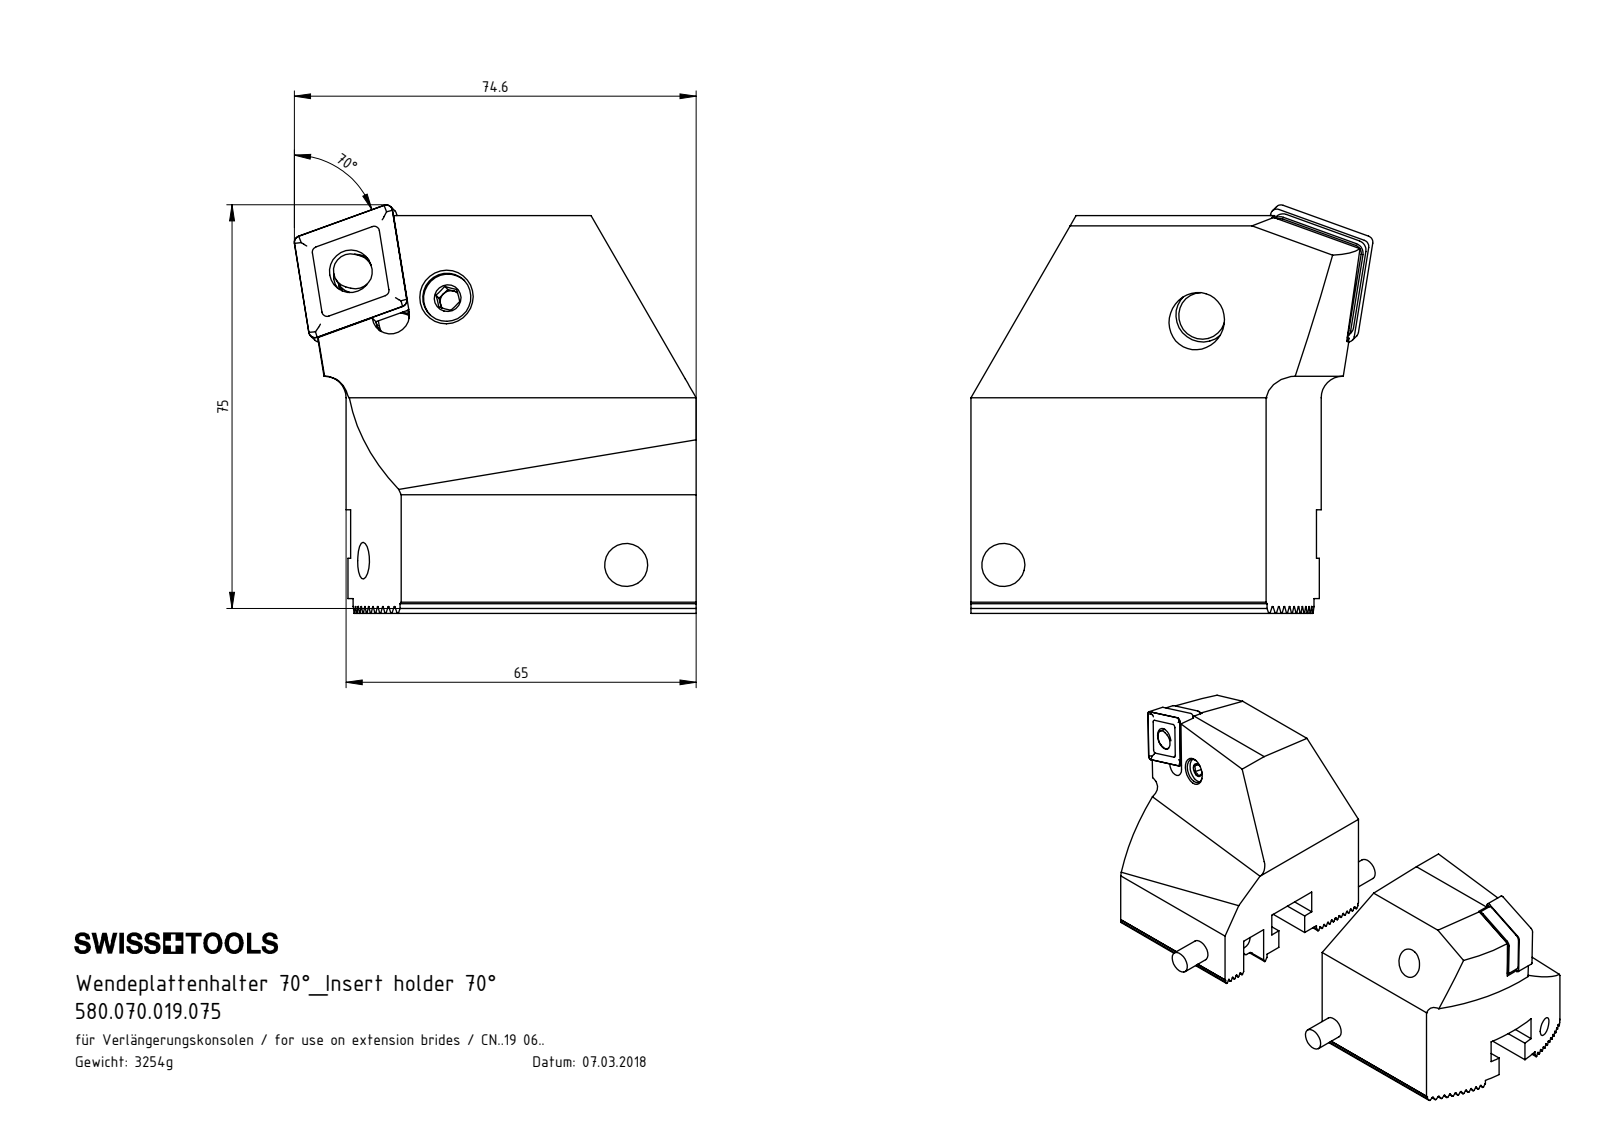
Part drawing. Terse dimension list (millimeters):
name: WCF-ER1.101.000; WCF; WCF-ER3.101.000_A; CNMG190612 (+6 more)
written by: SolidWorks 2017 (CONFIG_CONTROL_DESIGN)
unit: mm
bodies: 18 solids, 1312 faces (784 planar, 172 cylindrical, 356 other)
size: 200.21 × 94 × 75.79
volume: 411 183 mm³; area: 74 323 mm²
holes: 4× ⌀8, 2× ⌀6.8, 2× ⌀7.94, 2× ⌀9, 2× ⌀9.6, 2× ⌀10.2
bosses: 2× ⌀10, 2× ⌀9.9, 2× ⌀8.6, 2× ⌀8, 2× ⌀5.5, 2× ⌀4.45
rounds: 22× R0.14, 8× R1.2, 8× R1.8, 8× R4.15, 3× R4.7, 2× R3.1, 2× R3.5, 2× R3.65
face distances: 1.73, 6.93, 8.66, 70, 3.46, 5.2, 41.57, 43.3, 24.5, 45.5
hole spacings: 7, 18.55, 70, 18.8, 18.81, 40, 63, 77
